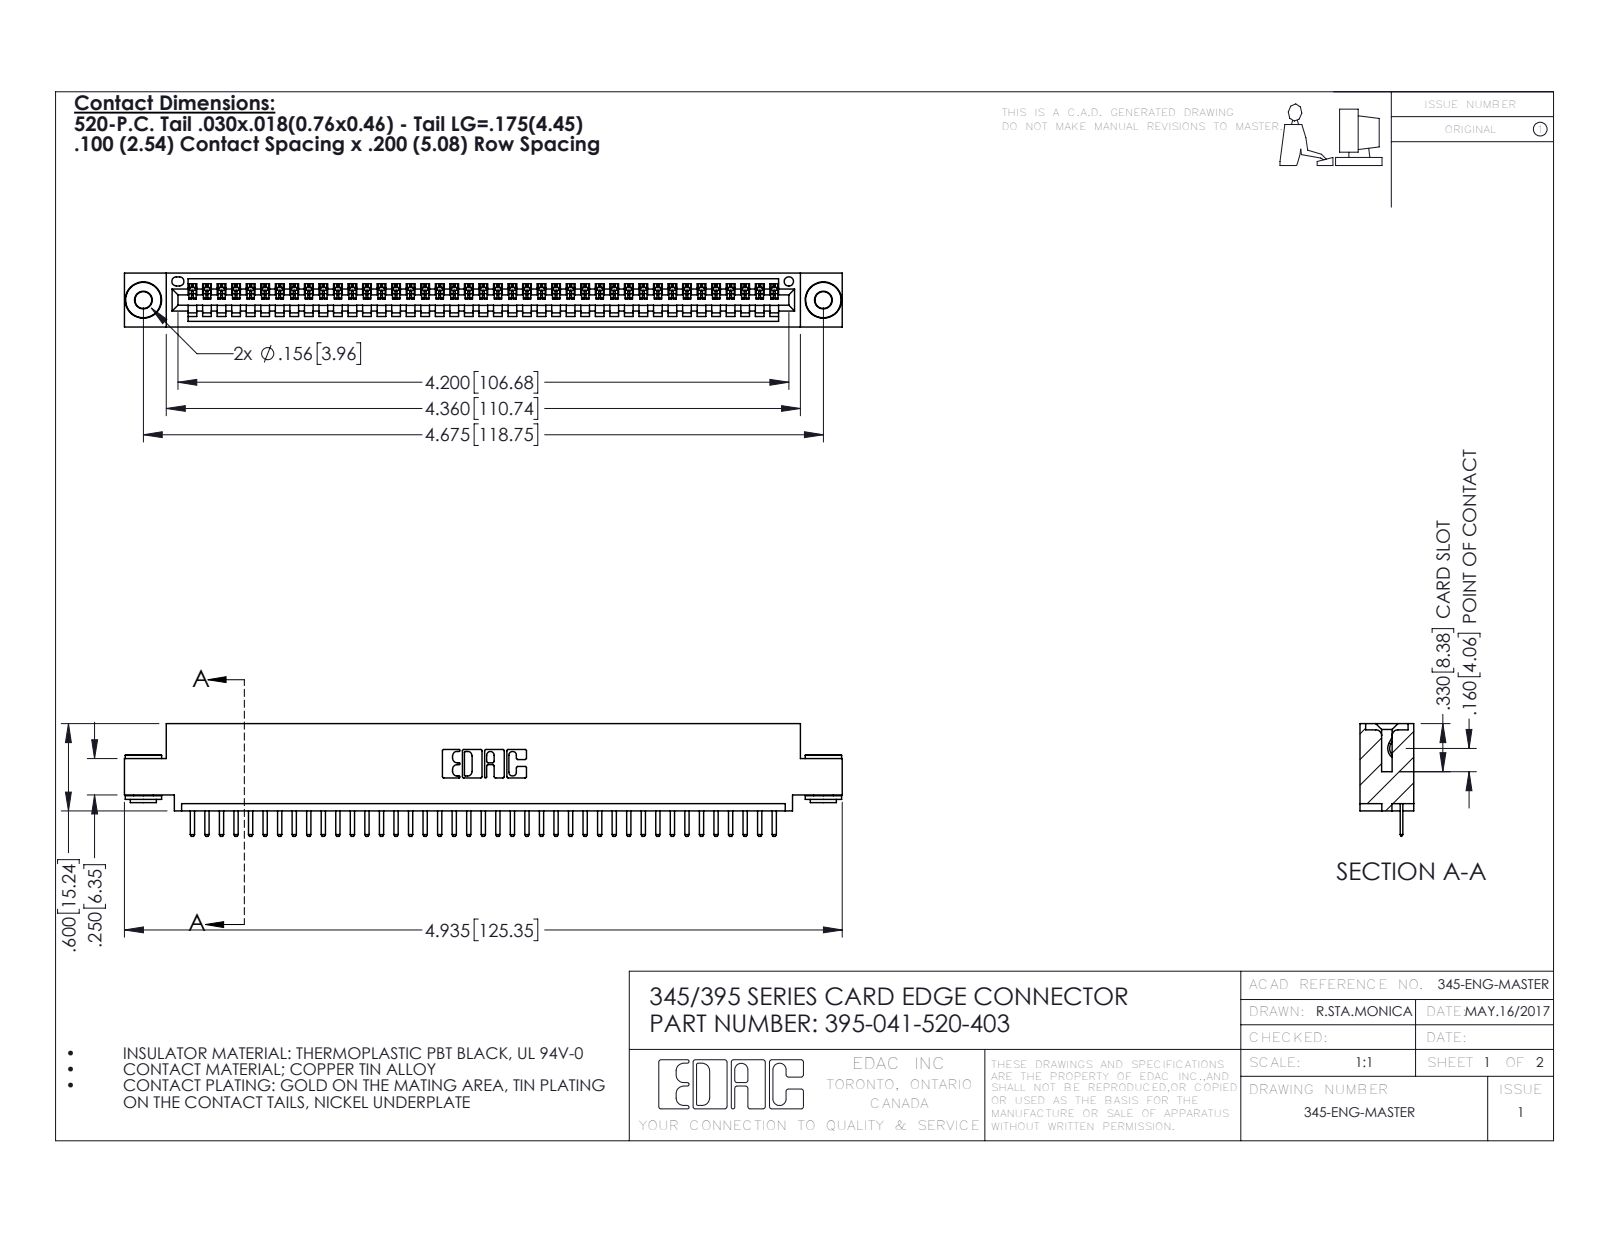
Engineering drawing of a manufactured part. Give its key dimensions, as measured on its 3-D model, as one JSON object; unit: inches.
{"part_name": "345 Part_0.110 Offset - 0.156 Dia-TH; 345-292-001_345-293-120; 395-041-520-403; 345-250-002_345-250-002-102", "step_written_by": "SolidWorks 2016 (CONFIG_CONTROL_DESIGN)", "units": "inches", "bodies": {"solids": 44, "faces": 2710, "planar": 1816, "cylindrical": 886, "other": 8}, "overall_size": [4.935, 0.775, 0.37], "volume_in3": 0.716, "surface_area_in2": 23.99, "round_holes": [[0.116, 2], [0.156, 2], [0.064, 1]], "round_bosses_or_shafts": [[0.25, 2], [0.18, 2], [0.136, 2]], "partial_cylinders_radius": [[0.01, 84], [0.006, 82], [0.01, 22], [0.007, 6], [0.031, 6], [0.026, 3], [0.031, 2], [0.04, 2]], "face_to_face_distances": [0.072, 0.298, 0.37, 0.2, 0.025, 0.098, 0.272, 0.225, 0.072, 0.149], "hole_center_spacings": [0.27, 4.439, 4.675]}
